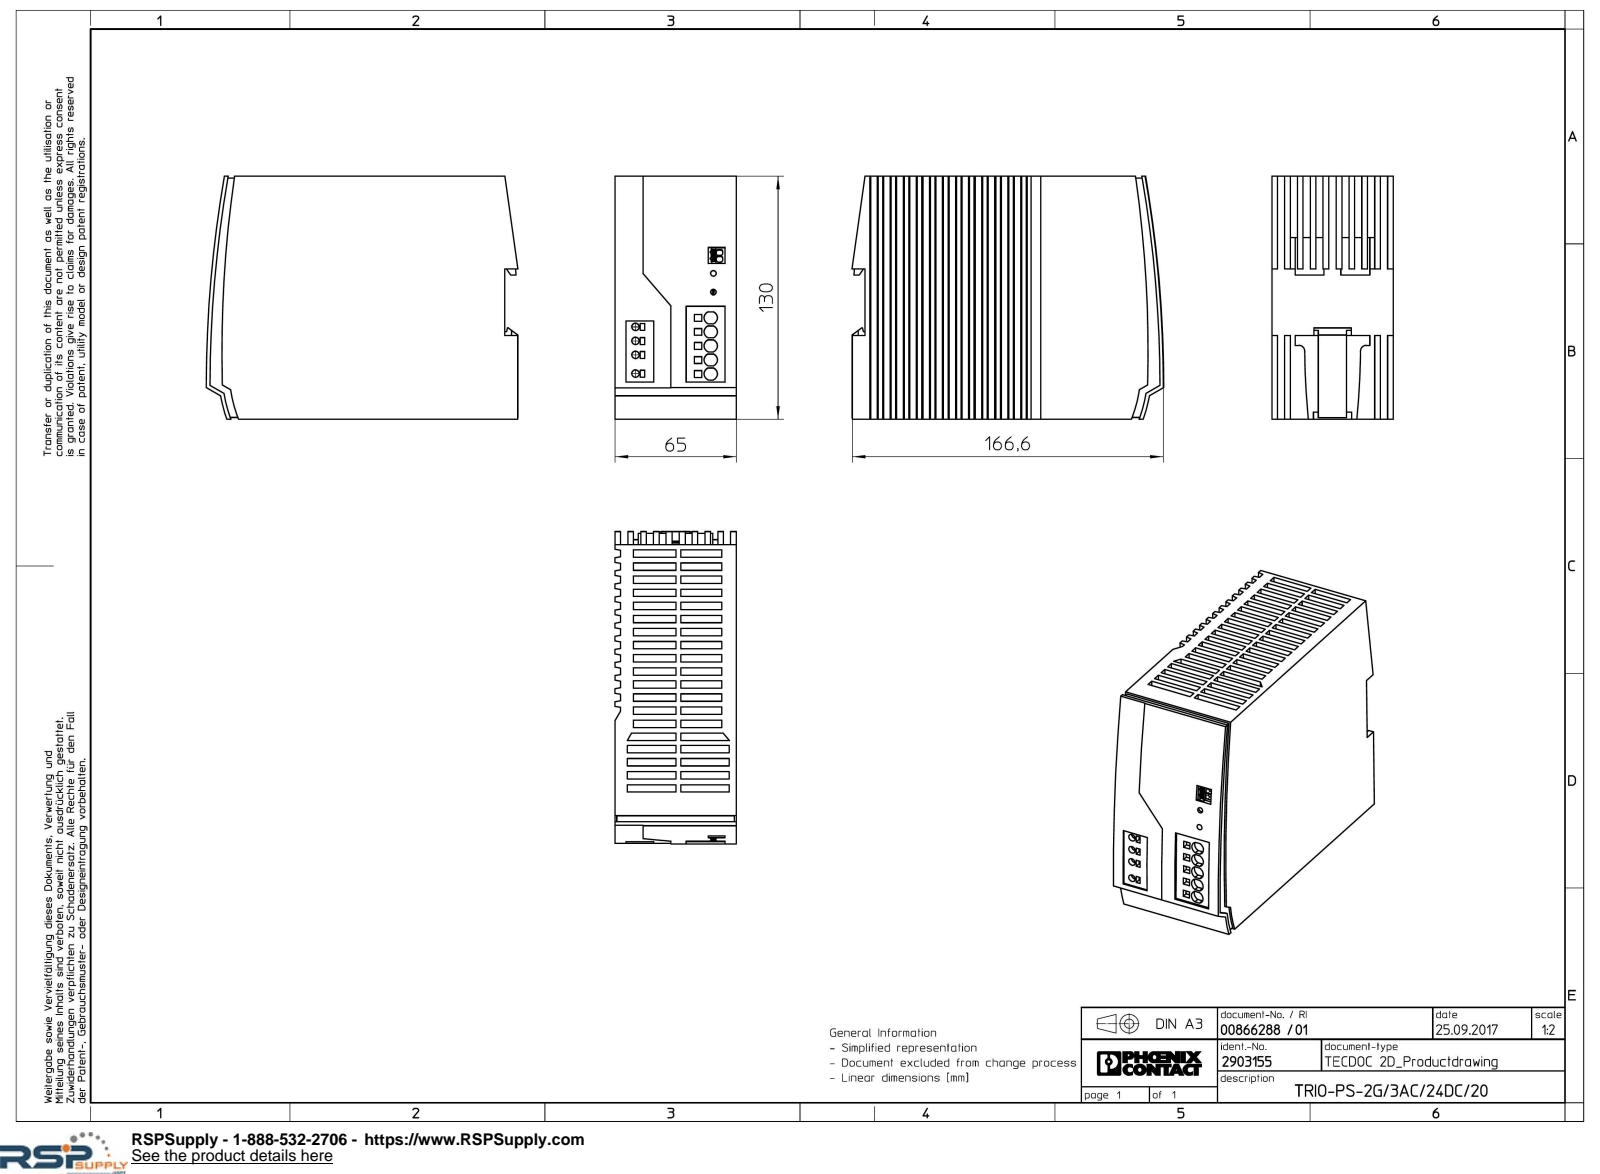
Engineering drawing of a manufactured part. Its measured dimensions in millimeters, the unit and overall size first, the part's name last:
Units: millimetres
Overall size (bounding box): 167 × 130 × 65
Round holes (diameter × count): ⌀4 ×4, ⌀3 ×2
Partial cylindrical surfaces — rounded edges, fillets, slot ends (radius × count): R3.45 ×10, R0.57 ×2, R0.6 ×2, R1.03 ×2, R1.04 ×2, R3 ×2, R430 ×2, R40 ×1
Main face-to-face distances: 3, 65, 13.79, 127, 27.58, 62, 6.89, 130, 41.37, 6.9
Hole centre spacings: 7.5, 10, 15, 17.5, 25
Volume: 1 292 000 mm³ · Surface area: 106 970 mm²
Bodies: 1 solid, 738 faces (686 planar, 47 cylindrical, 5 other)
Part name (STEP PRODUCT): TRIO_PS_2G_3AC_24DC_20-select
STEP written by: Creo Elements/Direct Modeling 18.1I 14-Aug-2016 (C) Parametric Technology GmbH (AUTOMOTIVE_DESIGN)
